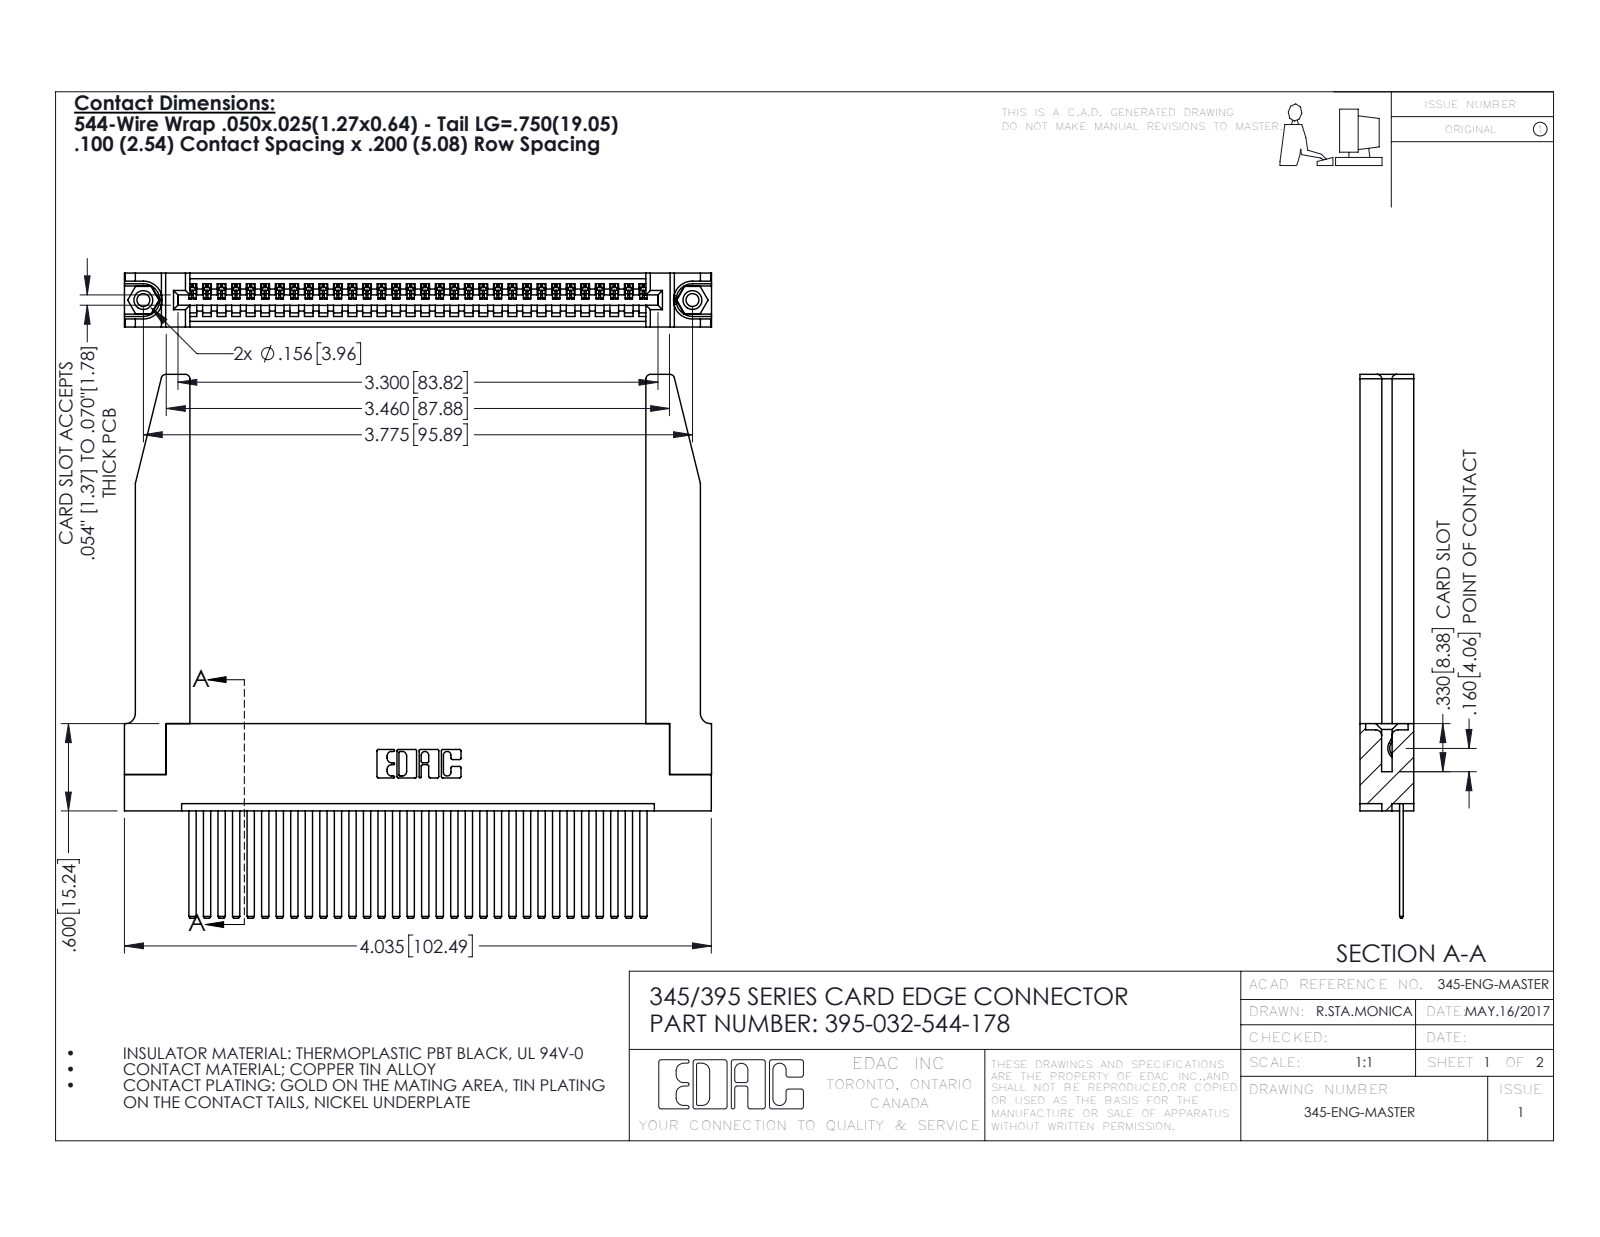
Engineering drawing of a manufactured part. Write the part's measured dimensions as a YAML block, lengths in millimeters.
part_name: "345-250-001_345-250-001-102; 395-032-544-178; 345-220-078_345-220-078; 345-292-001_345-293-144 (+1 more)"
step_written_by: "SolidWorks 2016 (CONFIG_CONTROL_DESIGN)"
units: millimeters
bodies: {solids: 37, faces: 2024, planar: 1374, cylindrical: 598, other: 52}
overall_size: [102.5, 94.9, 9.4]
volume: 17800
surface_area: 21150
round_holes:
  - {diameter: 2.3, count: 2}
  - {diameter: 3.2, count: 2}
  - {diameter: 4, count: 2}
  - {diameter: 1.6, count: 1}
round_bosses_or_shafts:
  - {diameter: 3.9, count: 2}
partial_cylinders:
  - {radius: 0.2, count: 64}
  - {radius: 0.3, count: 22}
  - {radius: 0.8, count: 8}
  - {radius: 0.2, count: 6}
  - {radius: 0.8, count: 6}
  - {radius: 0.7, count: 3}
  - {radius: 0.8, count: 2}
  - {radius: 1, count: 2}
face_to_face_distances: [1.8, 9.4, 7.6, 2.5, 6.9, 0.6, 5.1, 3.8, 3.8, 5.7]
hole_center_spacings: [6.9, 89.9, 95.9]
